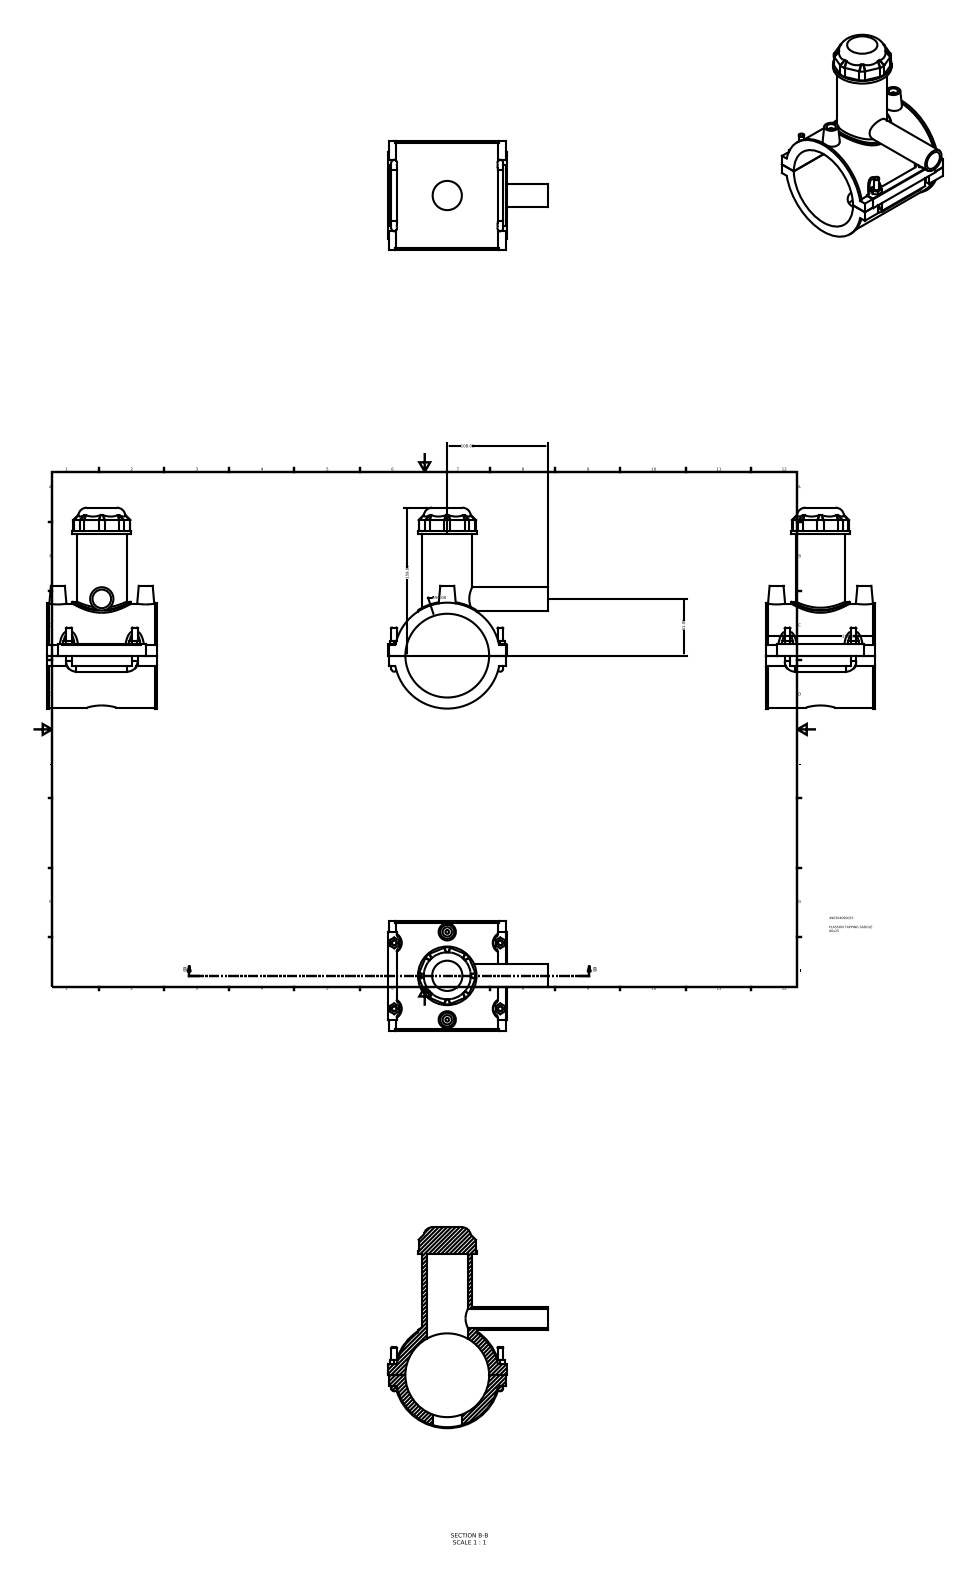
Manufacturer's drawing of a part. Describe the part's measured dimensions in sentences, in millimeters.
The part is named "496304090025". Its 3-D file was written by "Autodesk Inventor 2015 (AUTOMOTIVE_DESIGN)". It is 1 solid with 224 faces: 125 planar, 55 cylindrical and 44 other. Overall it measures 215.92 by 172 by 118 millimeters. Its volume is 575 149 cubic millimeters and its surface area 146 066 square millimeters. Round holes: 2 of diameter 10, 1 of diameter 20, 1 of diameter 31.36, 1 of diameter 44.1, 1 of diameter 90. Round bosses or shafts: 6 of diameter 6, 2 of diameter 4, 1 of diameter 113.83, 1 of diameter 111.6, 1 of diameter 63, 1 of diameter 53.55, 1 of diameter 25. Partial cylindrical surfaces (rounded edges, fillets, slot ends): 8 of radius 9, 4 of radius 3, 4 of radius 7.5, 1 of radius 0.5, 1 of radius 58.03. The main face-to-face distances are 118, 1, 130.55, 130.45, 127, 11.2, 11.3, 141.75, 23.5, 12.3. The hole center spacings are 47.2, 94.4.
